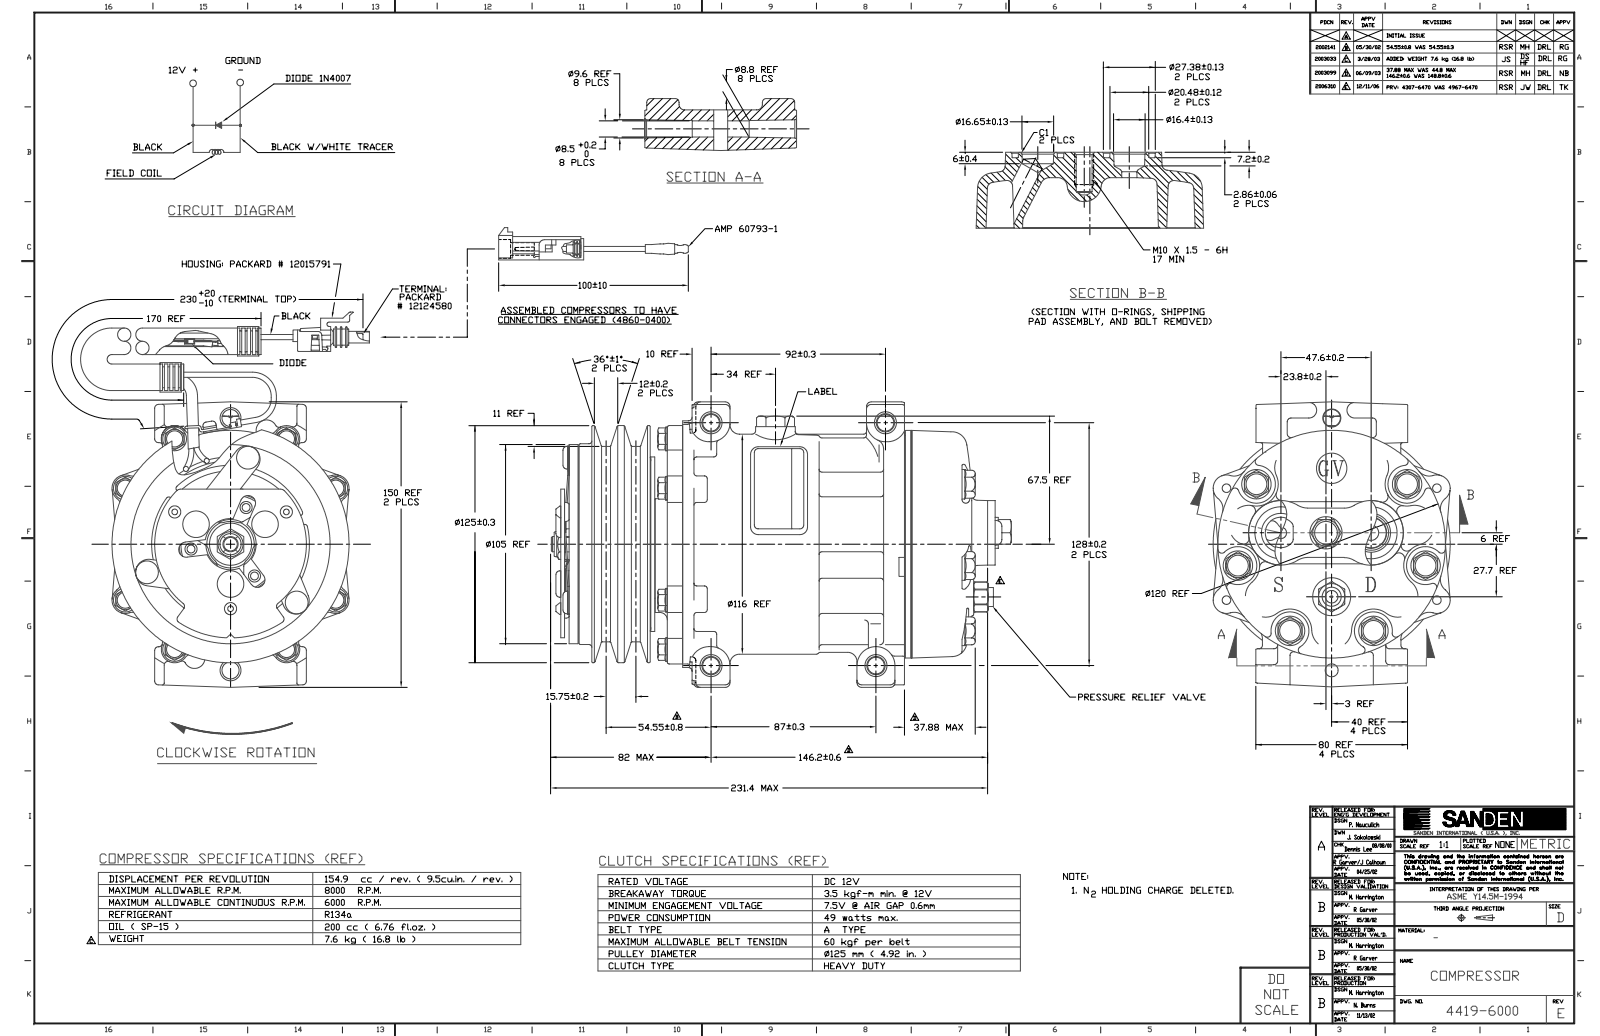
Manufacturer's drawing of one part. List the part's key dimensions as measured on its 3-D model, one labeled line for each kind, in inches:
Part name (STEP PRODUCT): SANDEN_4419_REV_F_COMPR_AC
STEP written by: SolidWorks 2007 (CONFIG_CONTROL_DESIGN)
Units: inches
Bodies: 1 solid, 2672 faces (721 planar, 685 cylindrical, 1266 other)
Overall size (bounding box): 17.749 × 9.096 × 4.921
Volume: 138 in³ · Surface area: 408.8 in²
Round holes (diameter × count): ⌀0.335 ×13, ⌀0.469 ×6, ⌀0.315 ×4, ⌀0.087 ×3, ⌀0.2 ×3, ⌀0.26 ×3, ⌀0.354 ×2, ⌀1.078 ×2, ⌀0.138 ×1, ⌀0.264 ×1, ⌀0.394 ×1, ⌀0.433 ×1
Round bosses / shafts (diameter × count): ⌀0.508 ×8, ⌀0.602 ×6, ⌀0.106 ×6, ⌀0.472 ×4, ⌀0.551 ×3, ⌀0.394 ×3, ⌀0.311 ×3, ⌀0.256 ×3
Partial cylindrical surfaces — rounded edges, fillets, slot ends (radius × count): R0.276 ×41, R0.079 ×39, R0.02 ×32, R0.118 ×30, R0.098 ×20, R0.059 ×18, R0.197 ×17, R0.394 ×15
Main face-to-face distances: 0.079, 0.22, 0.252, 0.197, 1.832, 1.572, 1.769, 0.173, 1.32, 0.512
Hole centre spacings: 2.474, 3.5, 1.239, 1.448, 1.827, 2.323, 2.626, 4.366
